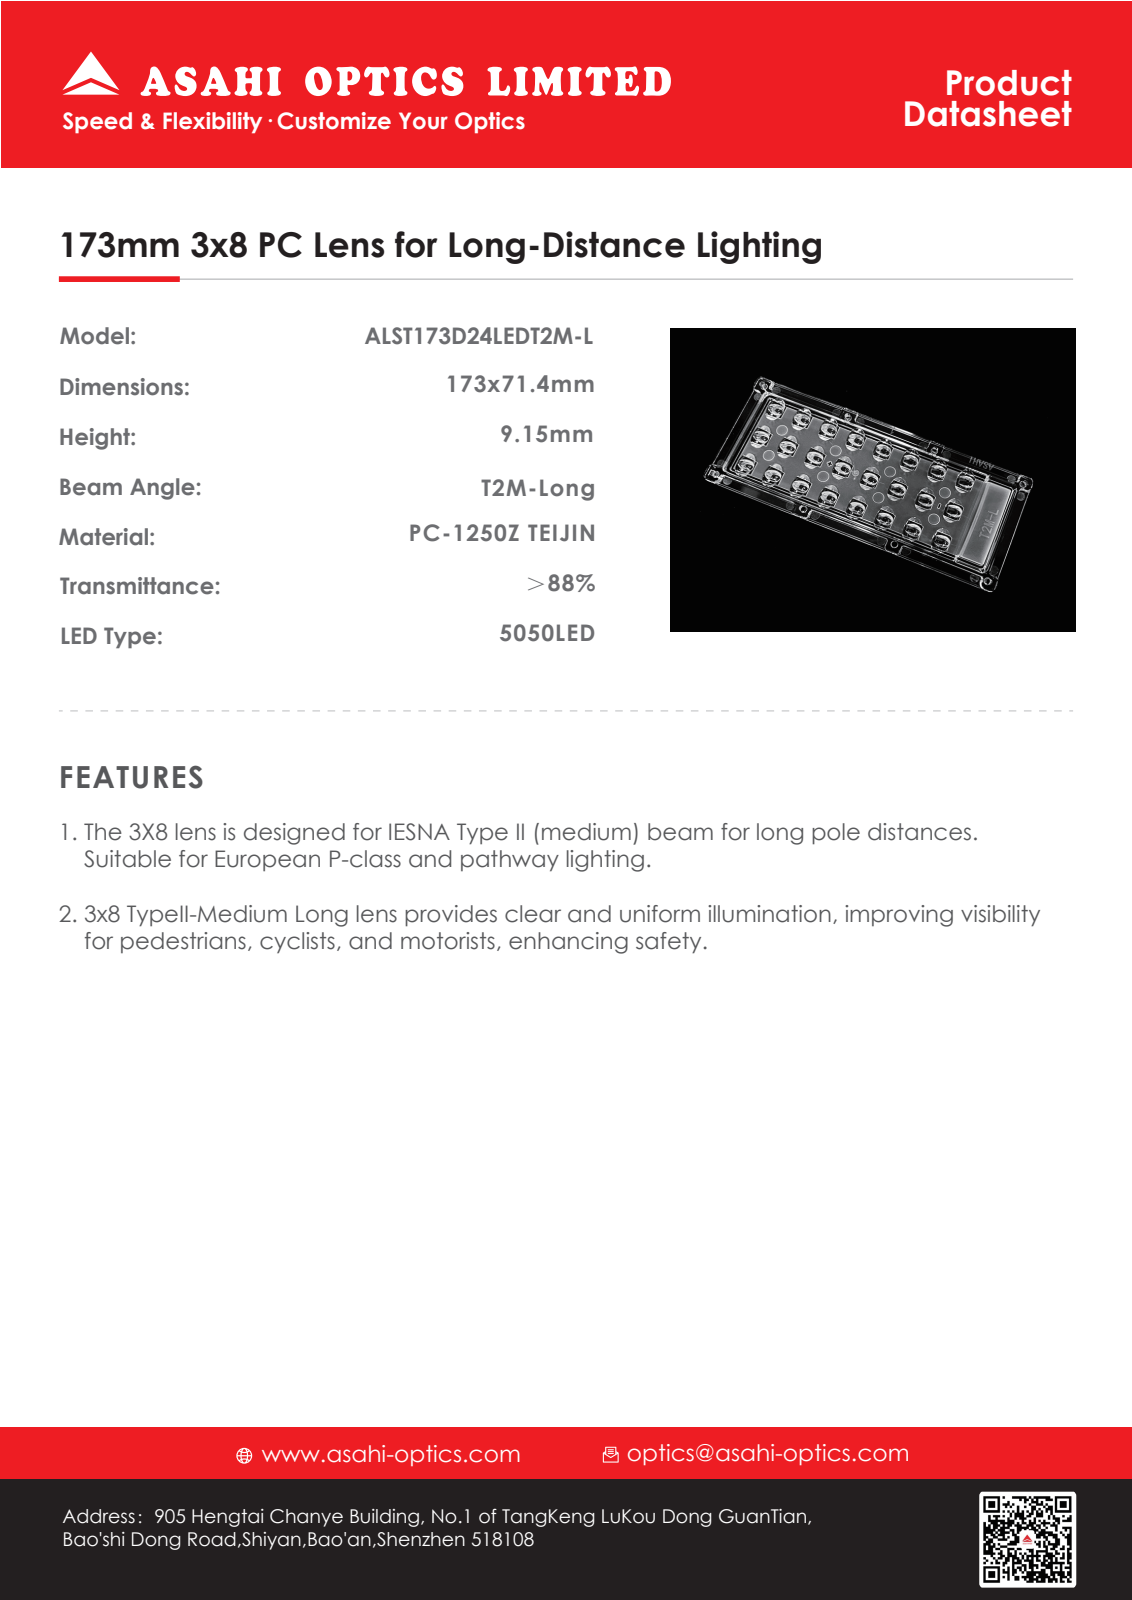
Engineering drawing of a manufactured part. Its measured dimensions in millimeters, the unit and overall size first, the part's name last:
Units: millimetres
Overall size (bounding box): 173 × 71.5 × 9.53
Partial cylindrical surfaces — rounded edges, fillets, slot ends (radius × count): R1 ×28, R0.5 ×24, R2 ×24, R3 ×12, R1.5 ×4, R4 ×4, R1.8 ×2, R2.5 ×2
Main face-to-face distances: 2.2, 1.5, 3.7, 2.65, 1.15, 1.05, 0.5, 1.7, 2.5, 2
Volume: 35 833 mm³ · Surface area: 33 078 mm²
Bodies: 1 solid, 852 faces (340 planar, 150 cylindrical, 362 other)
Part name (STEP PRODUCT): 24合1-T2M-NEW624_step
STEP written by: SIEMENS PLM Software NX 12.0 (AUTOMOTIVE_DESIGN)
